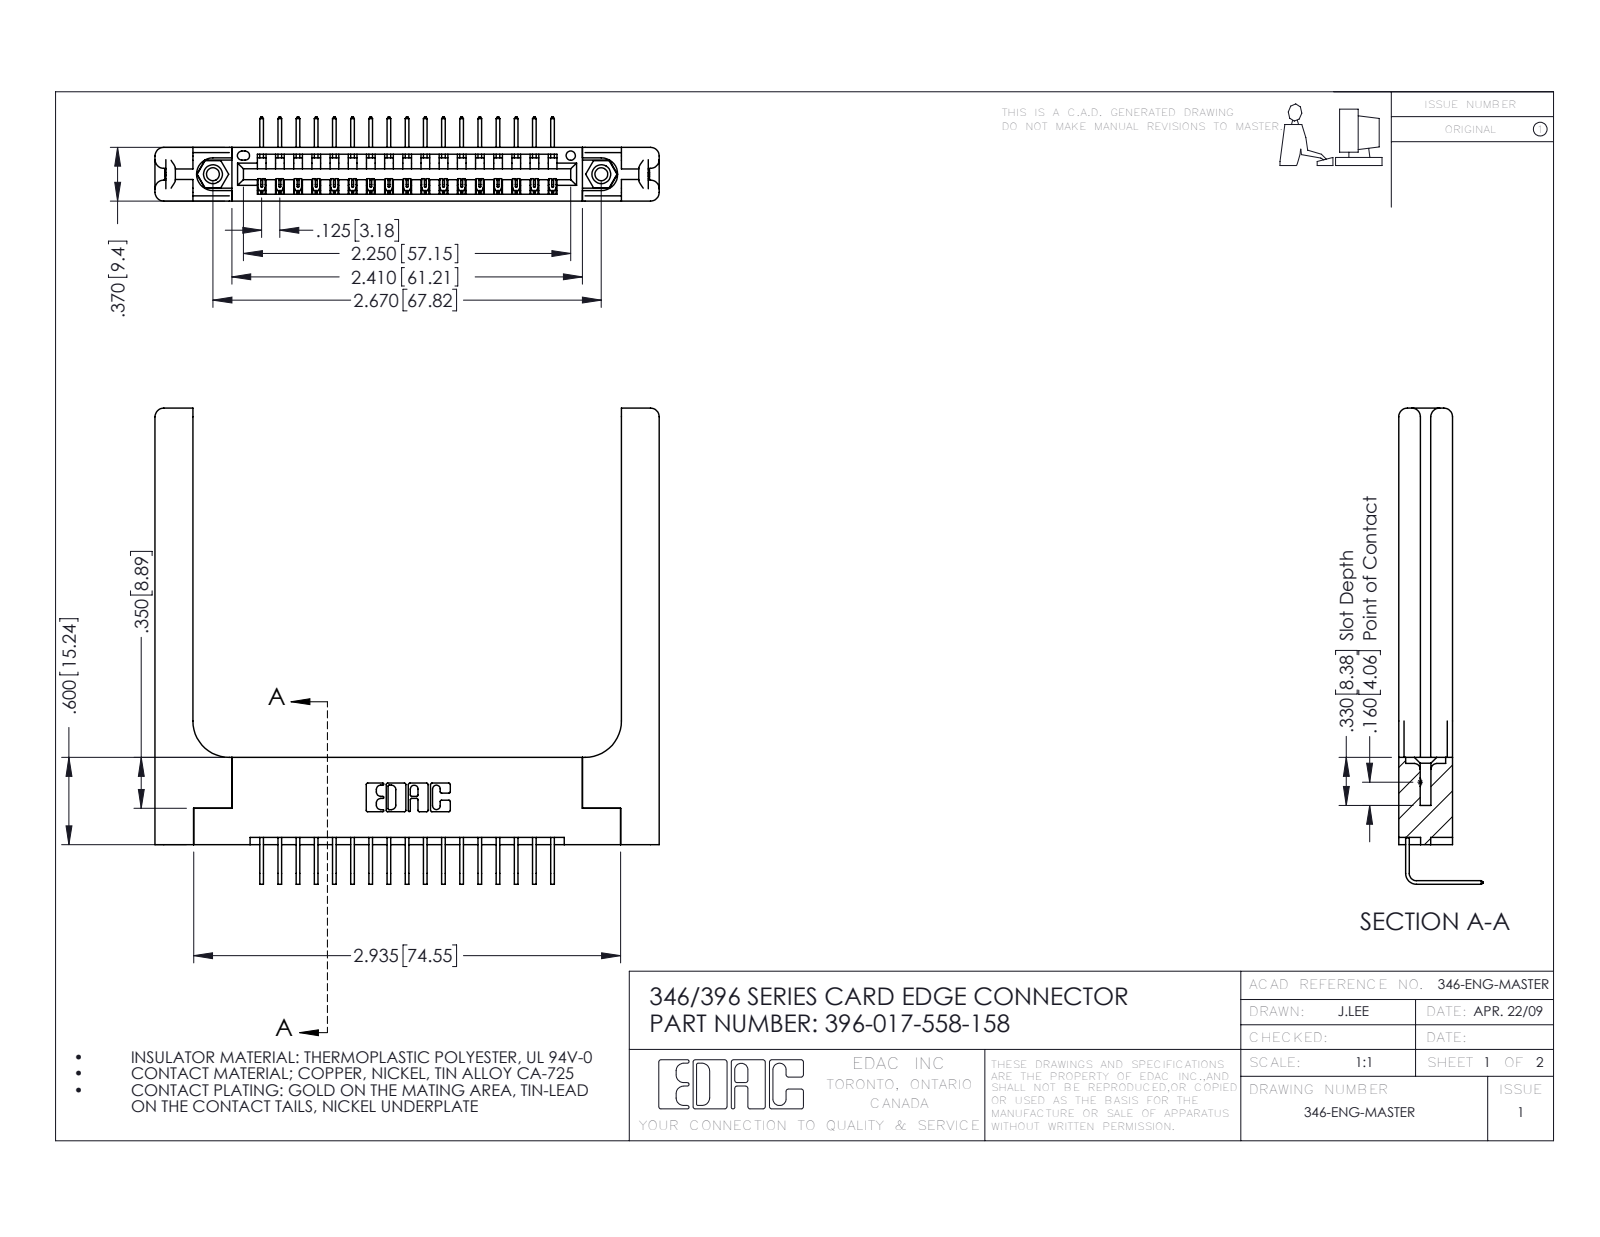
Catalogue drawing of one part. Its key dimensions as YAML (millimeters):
part_name: "345-292-001_558 Tail - 2; 346 Part_Flush Mounting Lugs - 0.156 Dia-TH; 346-220-058_345-220-058; 396-017-558-158 (+1 more)"
step_written_by: "SolidWorks 2016 (CONFIG_CONTROL_DESIGN)"
units: millimeters
bodies: {solids: 22, faces: 1398, planar: 938, cylindrical: 400, other: 60}
overall_size: [88, 83.1, 14.7]
volume: 15800
surface_area: 15630
round_holes:
  - {diameter: 2.3, count: 2}
  - {diameter: 3.2, count: 2}
  - {diameter: 4, count: 2}
  - {diameter: 1.6, count: 1}
round_bosses_or_shafts:
  - {diameter: 3.9, count: 2}
partial_cylinders:
  - {radius: 0.2, count: 34}
  - {radius: 0.3, count: 22}
  - {radius: 1.5, count: 16}
  - {radius: 0.2, count: 6}
  - {radius: 0.8, count: 6}
  - {radius: 0.7, count: 3}
  - {radius: 0.8, count: 2}
  - {radius: 0.8, count: 2}
face_to_face_distances: [9.4, 3.8, 1.8, 8.2, 3.8, 1.2, 6.4, 0.6, 7.6, 2.6]
hole_center_spacings: [6.2, 62.6, 67.8]
